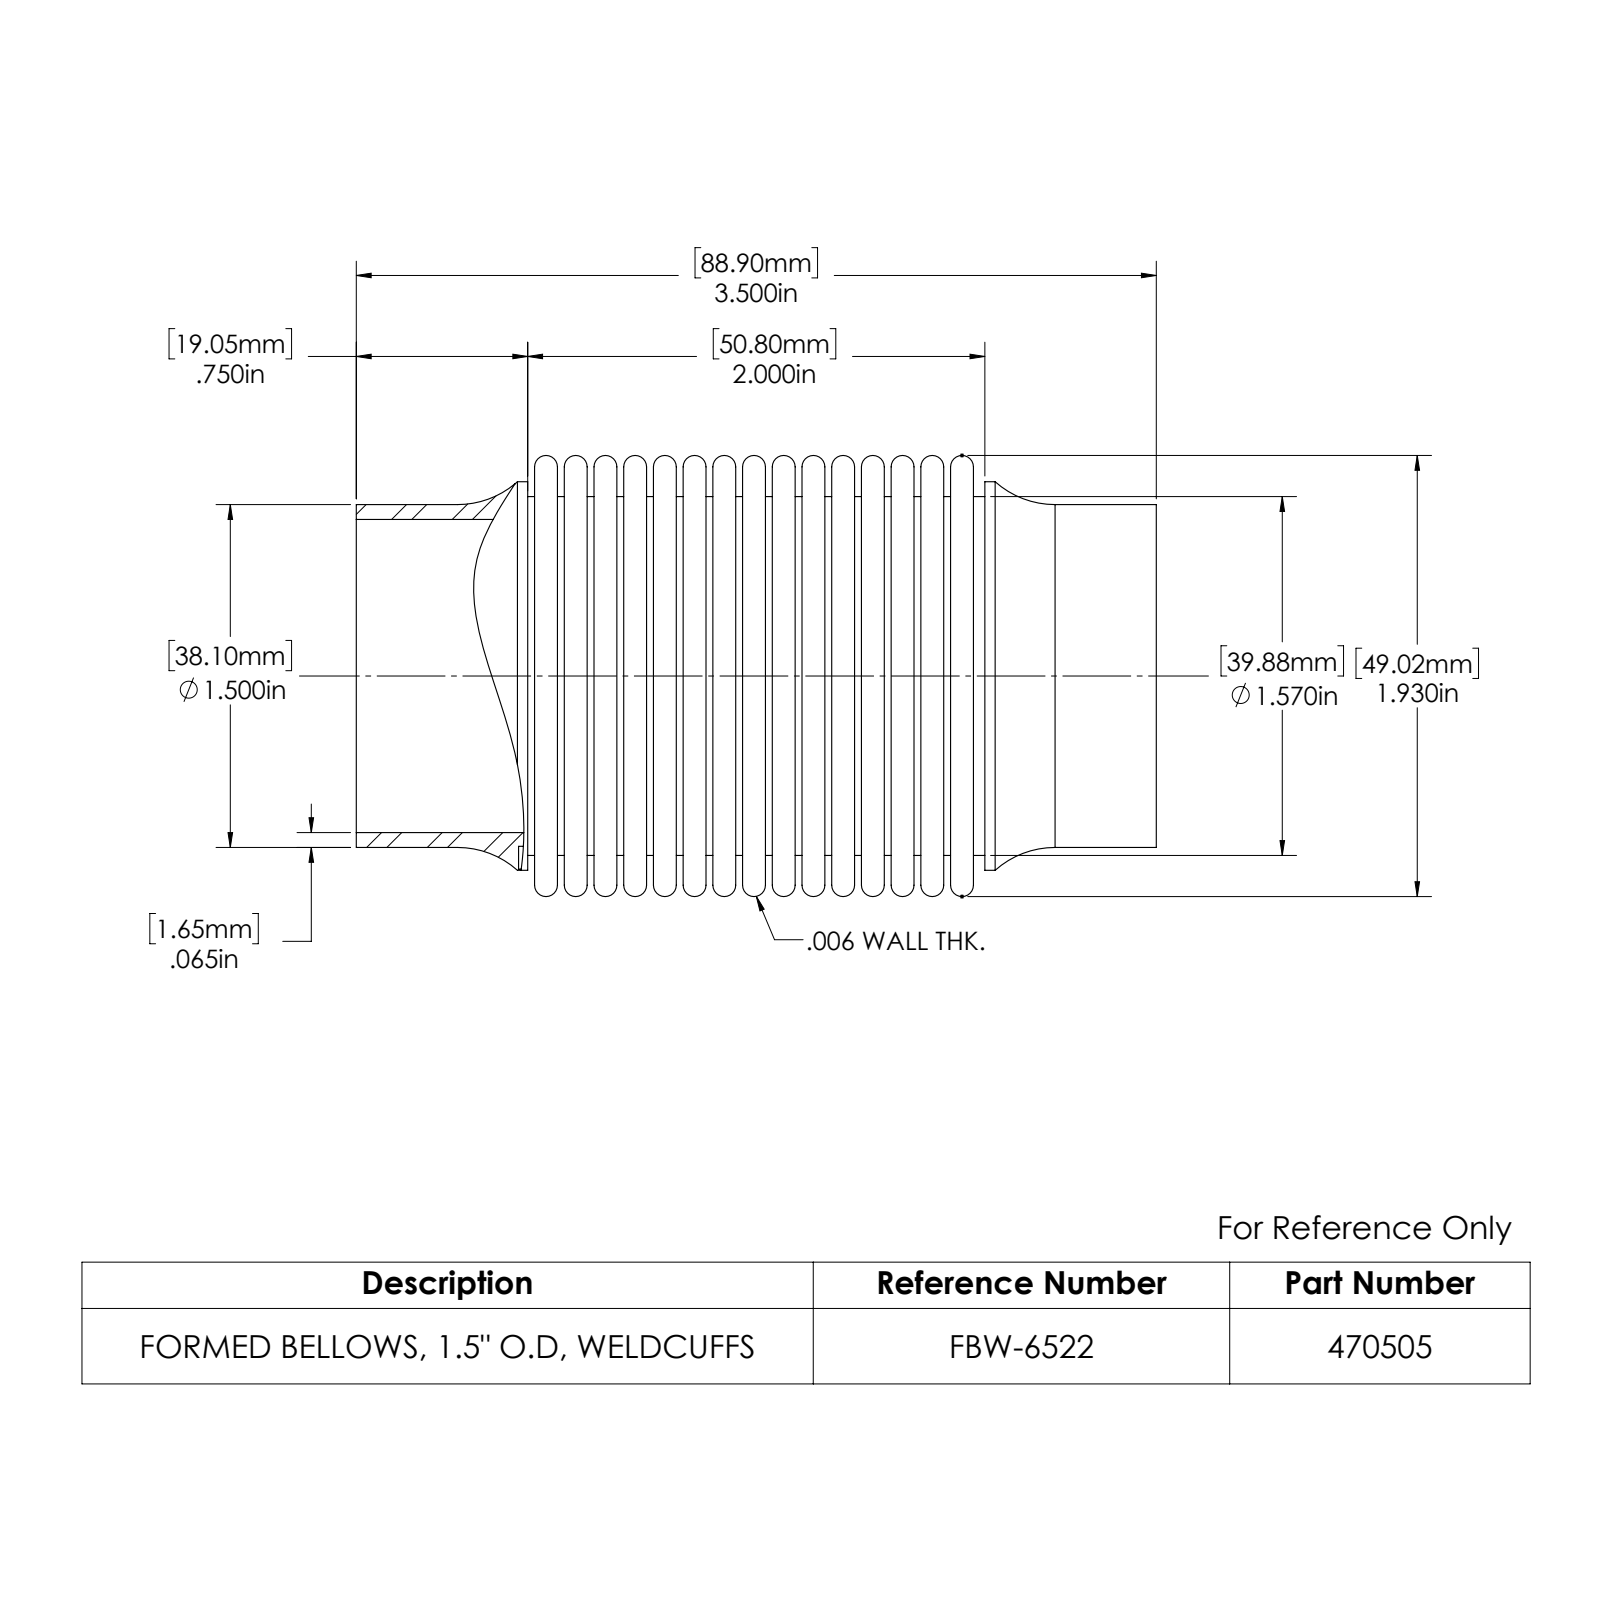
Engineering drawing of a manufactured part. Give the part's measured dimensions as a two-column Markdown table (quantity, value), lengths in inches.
| quantity | value |
| --- | --- |
| part name | 470505 |
| STEP written by | SolidWorks 2022 (AUTOMOTIVE_DESIGN) |
| units | inches |
| bodies | 1 solid, 218 faces (70 planar, 84 cylindrical, 64 other) |
| overall size | 3.5 × 1.93 × 1.93 |
| volume | 0.715 in³ |
| surface area | 92.82 in² |
| round holes (diameter × count) | 1.37 × 1, 1.56 × 1, 1.69 × 1 |
| round bosses / shafts (diameter × count) | 1.7 × 1, 1.57 × 1, 1.5 × 1, 1.49 × 1 |
| main face-to-face distances | 0.13, 0.26, 0.65, 0.78, 0.52, 0.39, 0.91, 0.39, 1.3, 1.43 |
